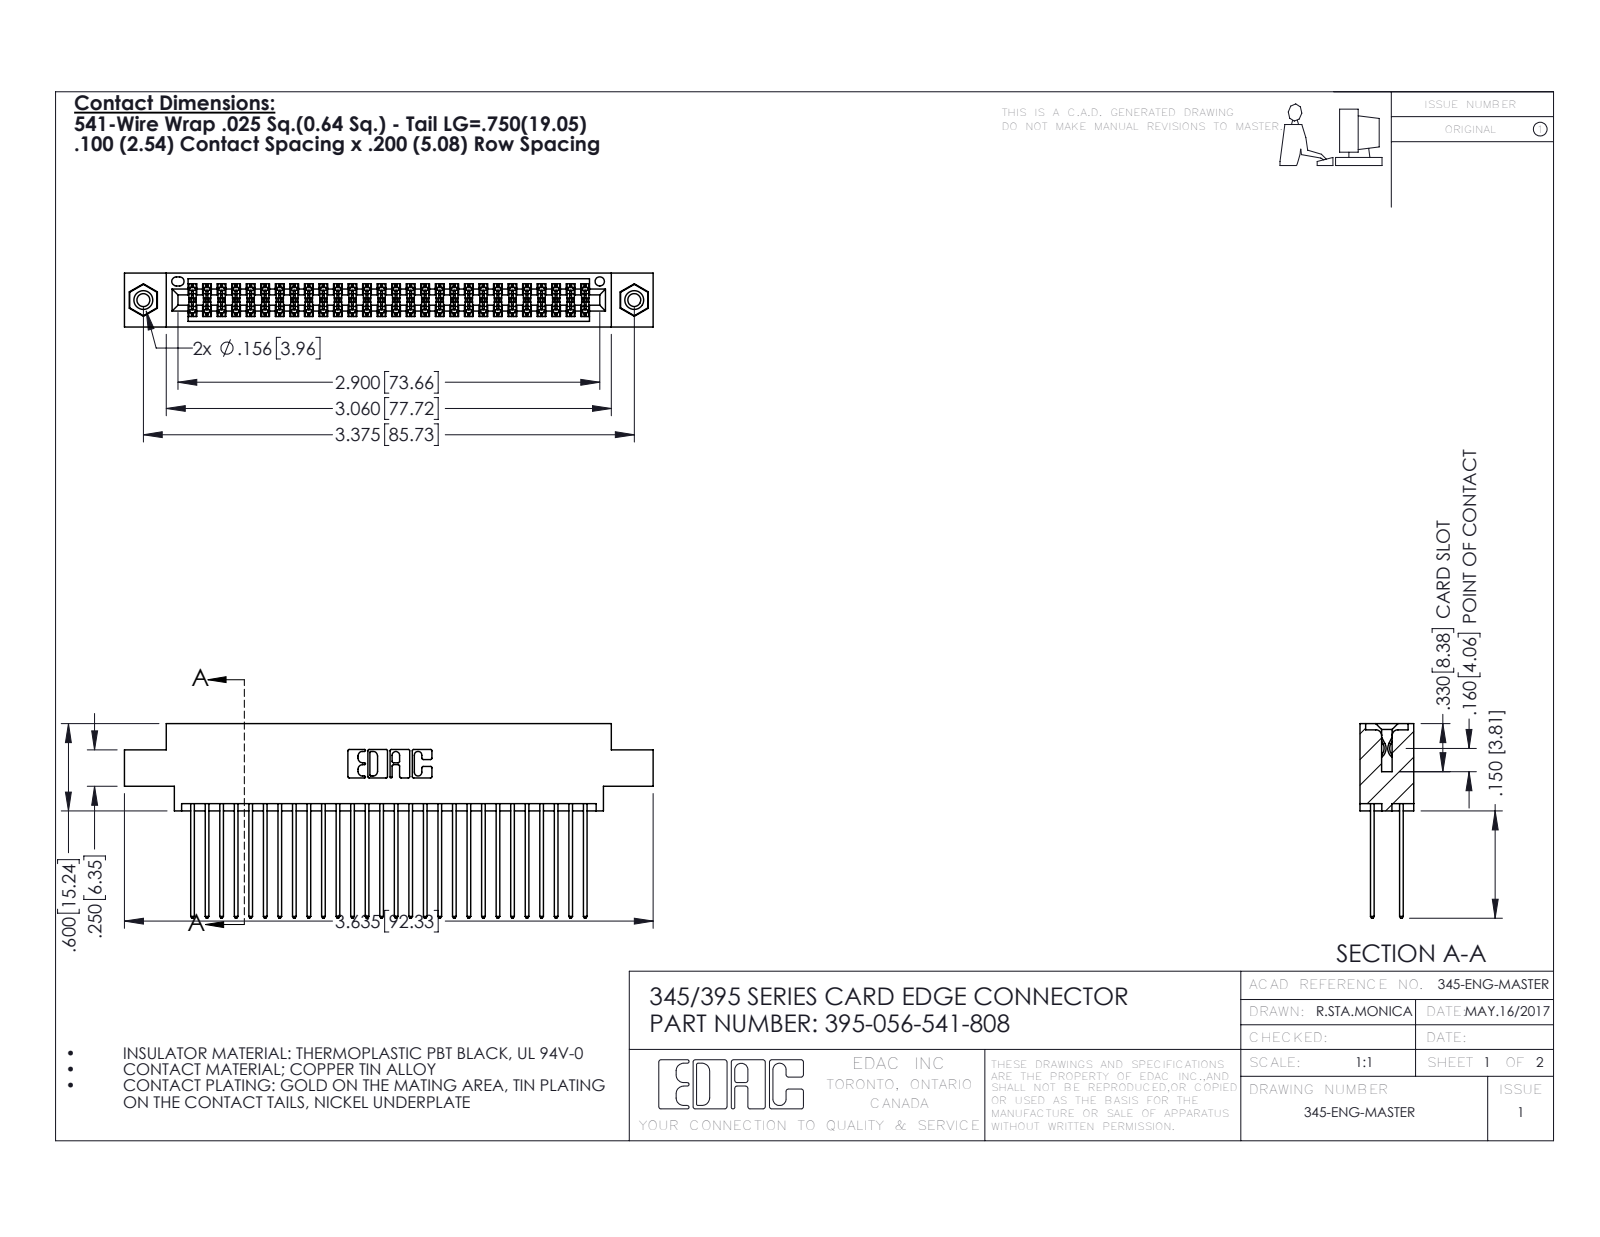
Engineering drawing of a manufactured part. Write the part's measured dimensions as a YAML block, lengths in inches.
part_name: "345 Part_0.170 Offset - 0.156 Dia-TI; 345-250-001_345-250-003-102; 345-292-001_345-293-141; 395-056-541-808"
step_written_by: "SolidWorks 2016 (CONFIG_CONTROL_DESIGN)"
units: inches
bodies: {solids: 59, faces: 2990, planar: 1964, cylindrical: 1010, other: 16}
overall_size: [3.635, 1.337, 0.37]
volume: 0.552
surface_area: 22.88
round_holes:
  - {diameter: 0.089, count: 2}
  - {diameter: 0.125, count: 2}
  - {diameter: 0.156, count: 2}
  - {diameter: 0.064, count: 1}
round_bosses_or_shafts:
  - {diameter: 0.155, count: 2}
partial_cylinders:
  - {radius: 0.006, count: 84}
  - {radius: 0.01, count: 56}
  - {radius: 0.01, count: 22}
  - {radius: 0.007, count: 6}
  - {radius: 0.031, count: 6}
  - {radius: 0.026, count: 3}
  - {radius: 0.014, count: 2}
  - {radius: 0.019, count: 2}
face_to_face_distances: [0.072, 0.298, 0.2, 0.098, 0.272, 0.025, 0.37, 0.225, 0.175, 0.149]
hole_center_spacings: [0.27, 3.14, 3.375]
